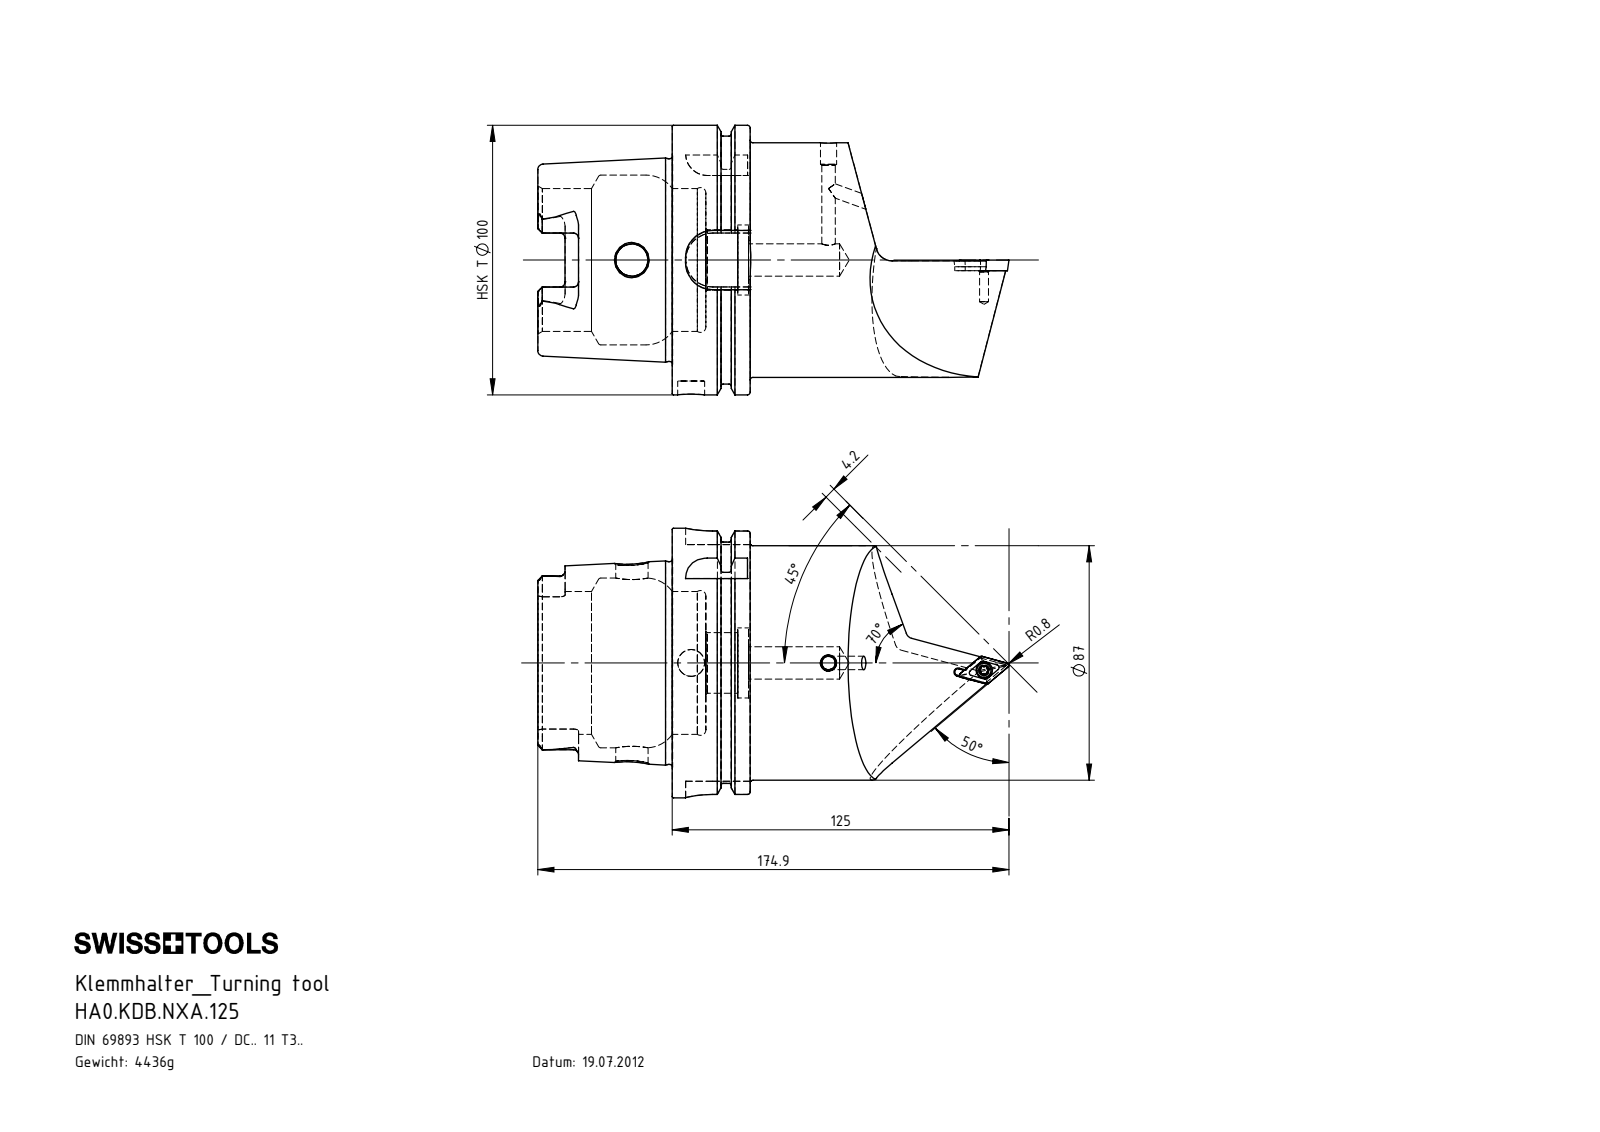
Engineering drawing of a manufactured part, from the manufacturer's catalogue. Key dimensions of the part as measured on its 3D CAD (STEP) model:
Part name (STEP PRODUCT): HA0-KDB.NXA.125_A; HA0.KDB.NXA.125; KVT_MB_600_060; WCB-ER2.001.009_A (+1 more)
STEP written by: SolidWorks 2022 (AUTOMOTIVE_DESIGN)
Units: millimetres
Bodies: 5 solids, 303 faces (76 planar, 88 cylindrical, 139 other)
Overall size (bounding box): 174.91 × 100 × 100
Volume: 542 362 mm³ · Surface area: 67 876 mm²
Round holes (diameter × count): ⌀5 ×2, ⌀12 ×2, ⌀3.3 ×1, ⌀4.4 ×1, ⌀6.1 ×1, ⌀10 ×1, ⌀22.5 ×1, ⌀26 ×1, ⌀53 ×1, ⌀63 ×1
Round bosses / shafts (diameter × count): ⌀100 ×1, ⌀91.95 ×1, ⌀87 ×1, ⌀75.26 ×1, ⌀6 ×1, ⌀5.25 ×1, ⌀4 ×1
Partial cylindrical surfaces — rounded edges, fillets, slot ends (radius × count): R0.34 ×6, R0.59 ×6, R1.9 ×6, R4.88 ×4, R10 ×4, R0.8 ×1, R1.25 ×1, R6 ×1
Main face-to-face distances: 12.45, 28.95, 16.5, 49.9, 62.35, 78.85, 87.8, 78.2, 28.3, 15.85
Hole centre spacings: 43, 65.33, 65.43, 108.31, 108.41
